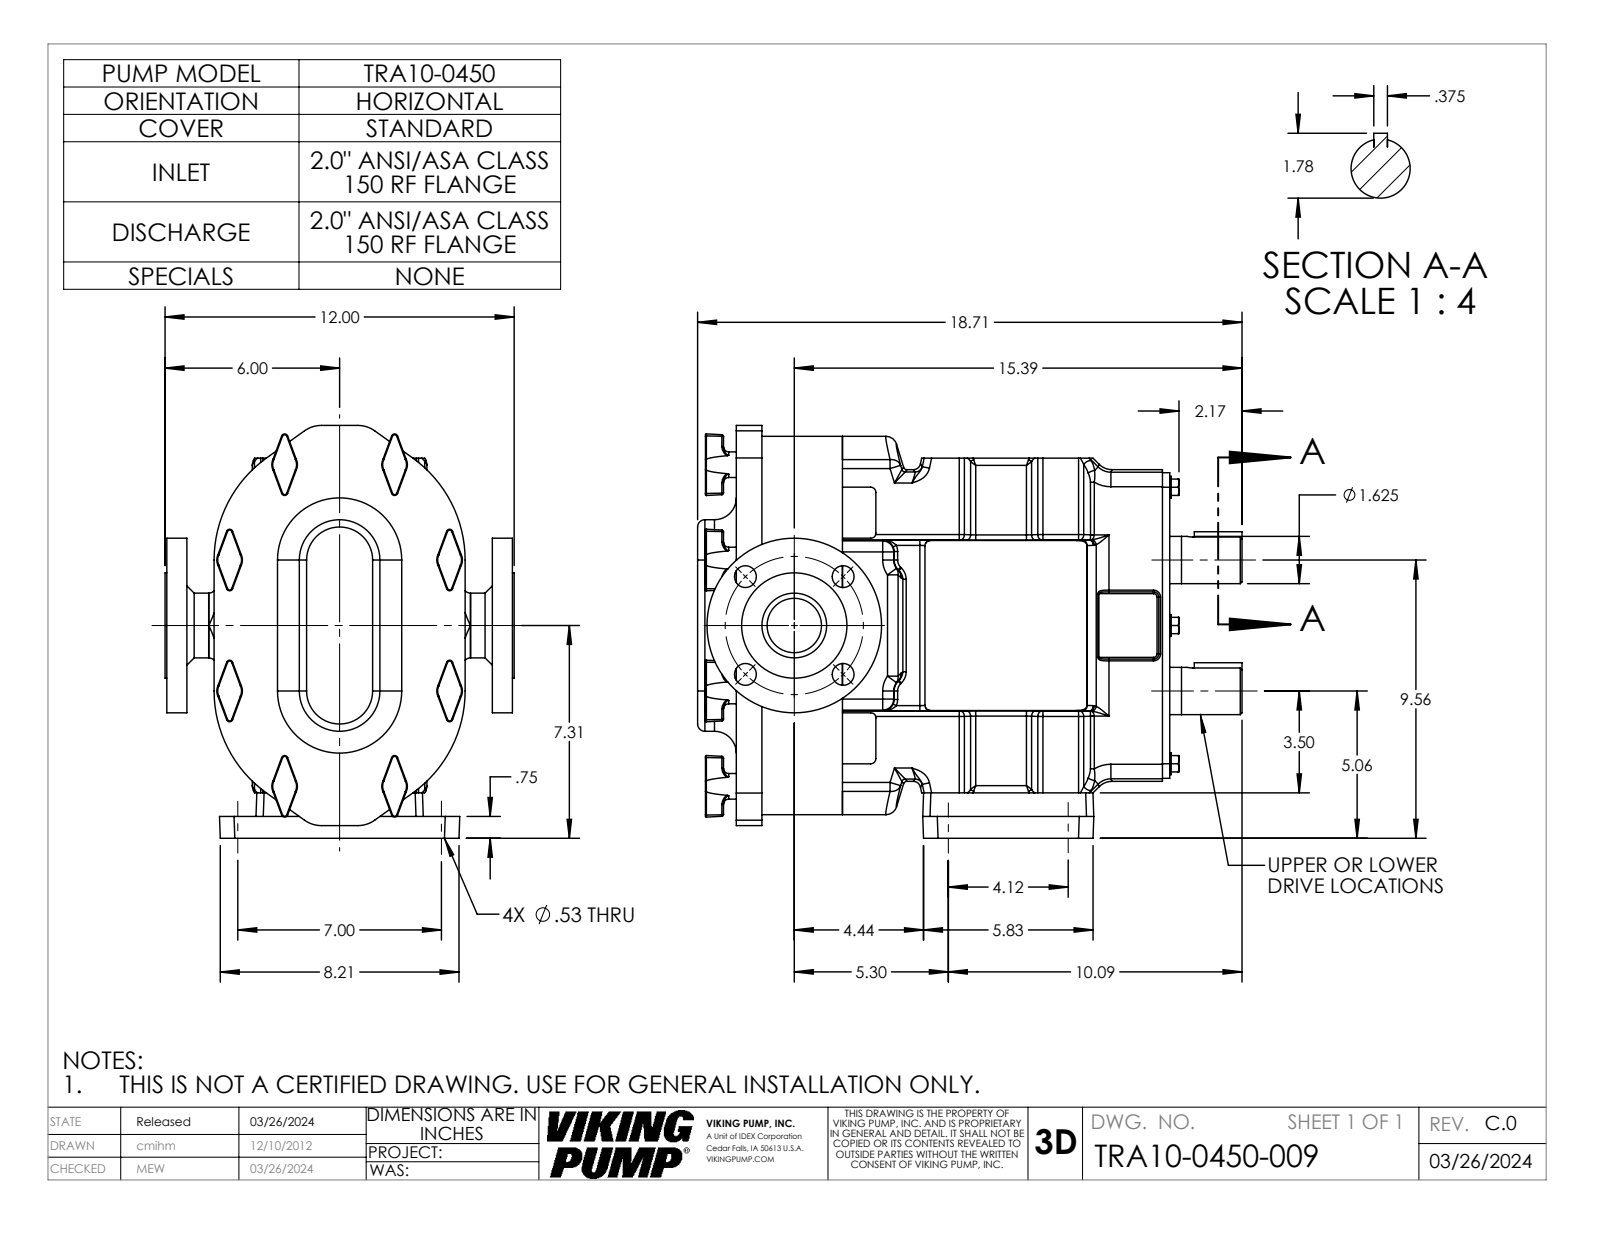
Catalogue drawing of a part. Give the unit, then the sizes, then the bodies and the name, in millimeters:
Units: millimetres
Overall size (bounding box): 475.3 × 360.3 × 304.8
Round holes (diameter × count): ⌀13.5 ×4, ⌀19.1 ×4, ⌀47.5 ×1, ⌀56.5 ×1
Round bosses / shafts (diameter × count): ⌀22.4 ×8, ⌀19.1 ×6, ⌀41.2 ×2, ⌀152.4 ×1, ⌀91.9 ×1
Partial cylindrical surfaces — rounded edges, fillets, slot ends (radius × count): R4.6 ×44, R1.5 ×43, R0.8 ×32, R6.4 ×32, R9.7 ×28, R3 ×24, R12.7 ×20, R9.5 ×12
Main face-to-face distances: 70.3, 12.7, 285.8, 19.1, 22.4, 92.7, 9.1, 378.4, 356.1, 165.1
Hole centre spacings: 60.3, 60.3, 85.3, 85.3, 104.6, 120.7, 177.8, 206.3
Volume: 19 940 000 mm³ · Surface area: 940 000 mm²
Bodies: 5 solids, 1056 faces (285 planar, 391 cylindrical, 380 other)
Part name (STEP PRODUCT): TRA10-0450-BODY; 0450FLG150-20; TRA10-0600-GEARBOX-H; TRA10-0600-COVER-STD (+1 more)
STEP written by: SolidWorks 2022 (AUTOMOTIVE_DESIGN)
